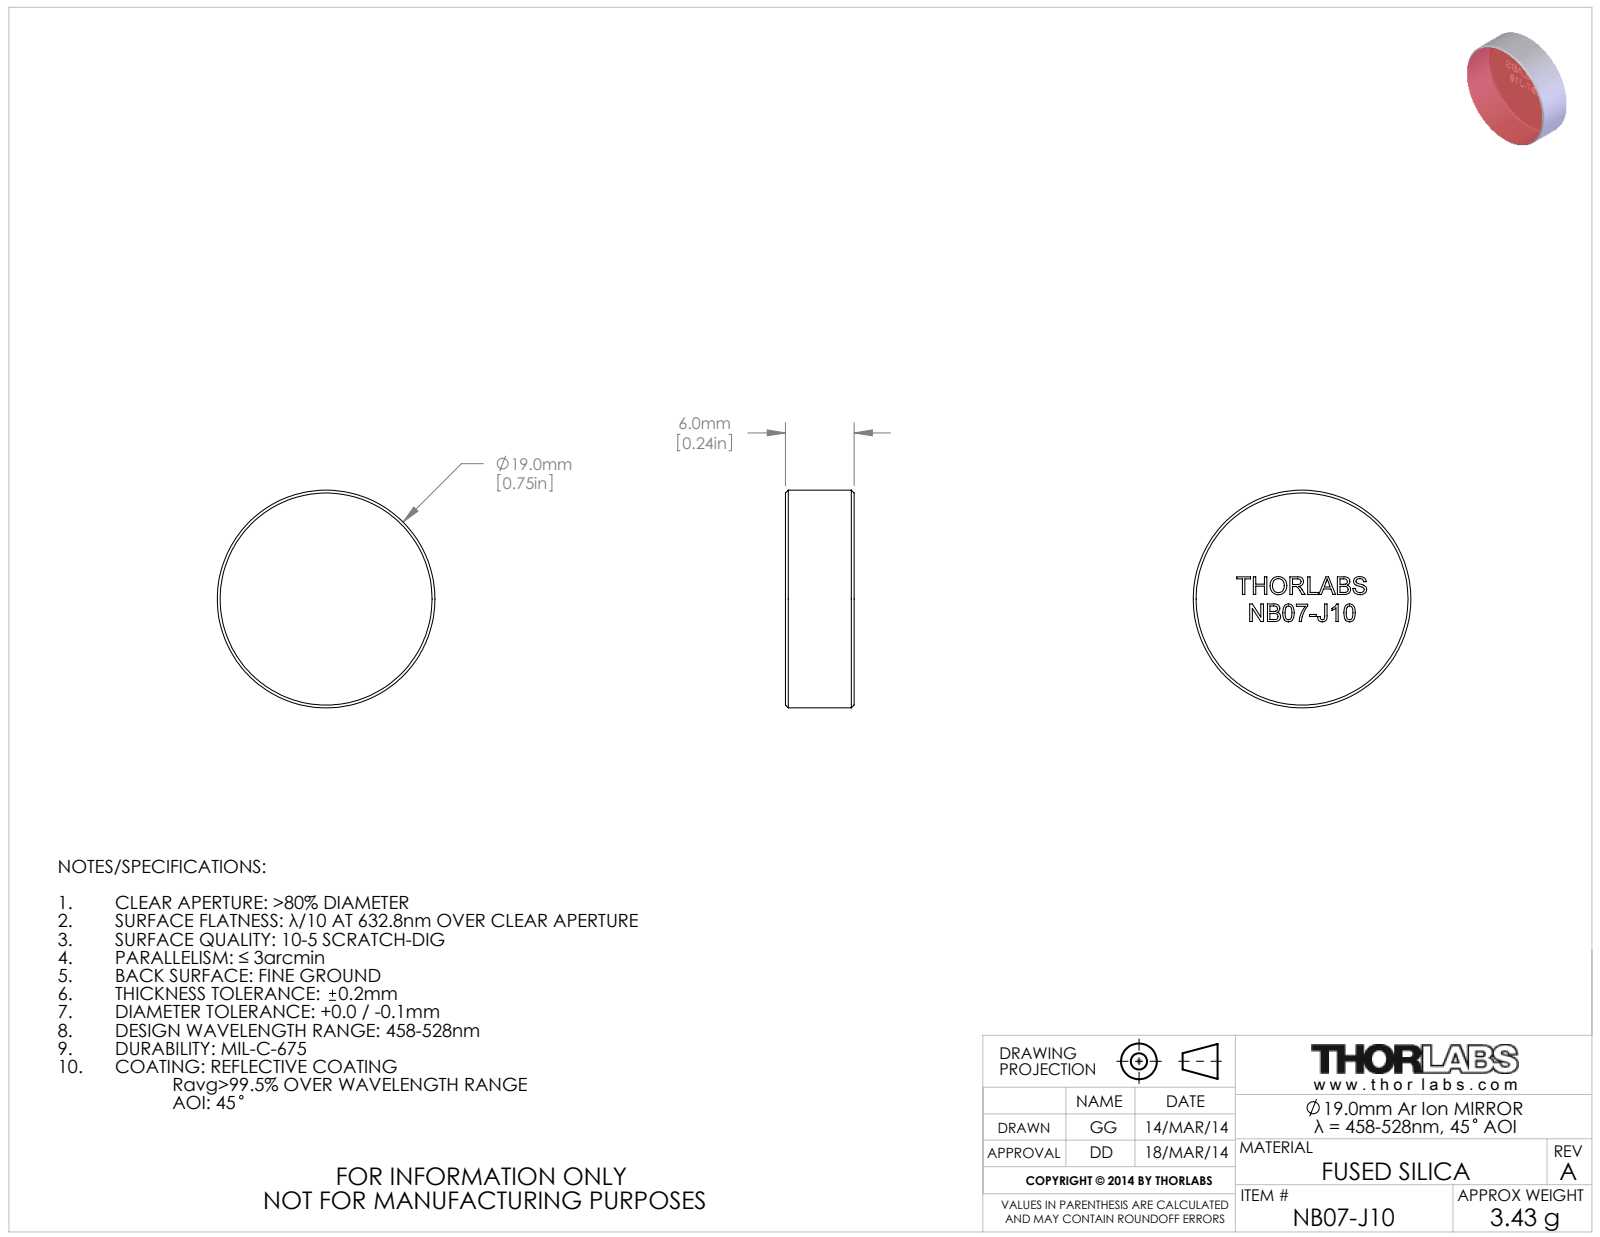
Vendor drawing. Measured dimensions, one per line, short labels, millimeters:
name: TTN024118-E0W
written by: SolidWorks 2012 (CONFIG_CONTROL_DESIGN)
unit: mm
bodies: 1 solid, 210 faces (123 planar, 2 cylindrical, 85 other)
size: 19 × 19 × 6
volume: 1 700 mm³; area: 908 mm²
bosses: 1× ⌀19
face distances: 6, 1.5, 1, 1.9, 2.4, 4.1, 0.3, 2.4, 1.2, 6.5
